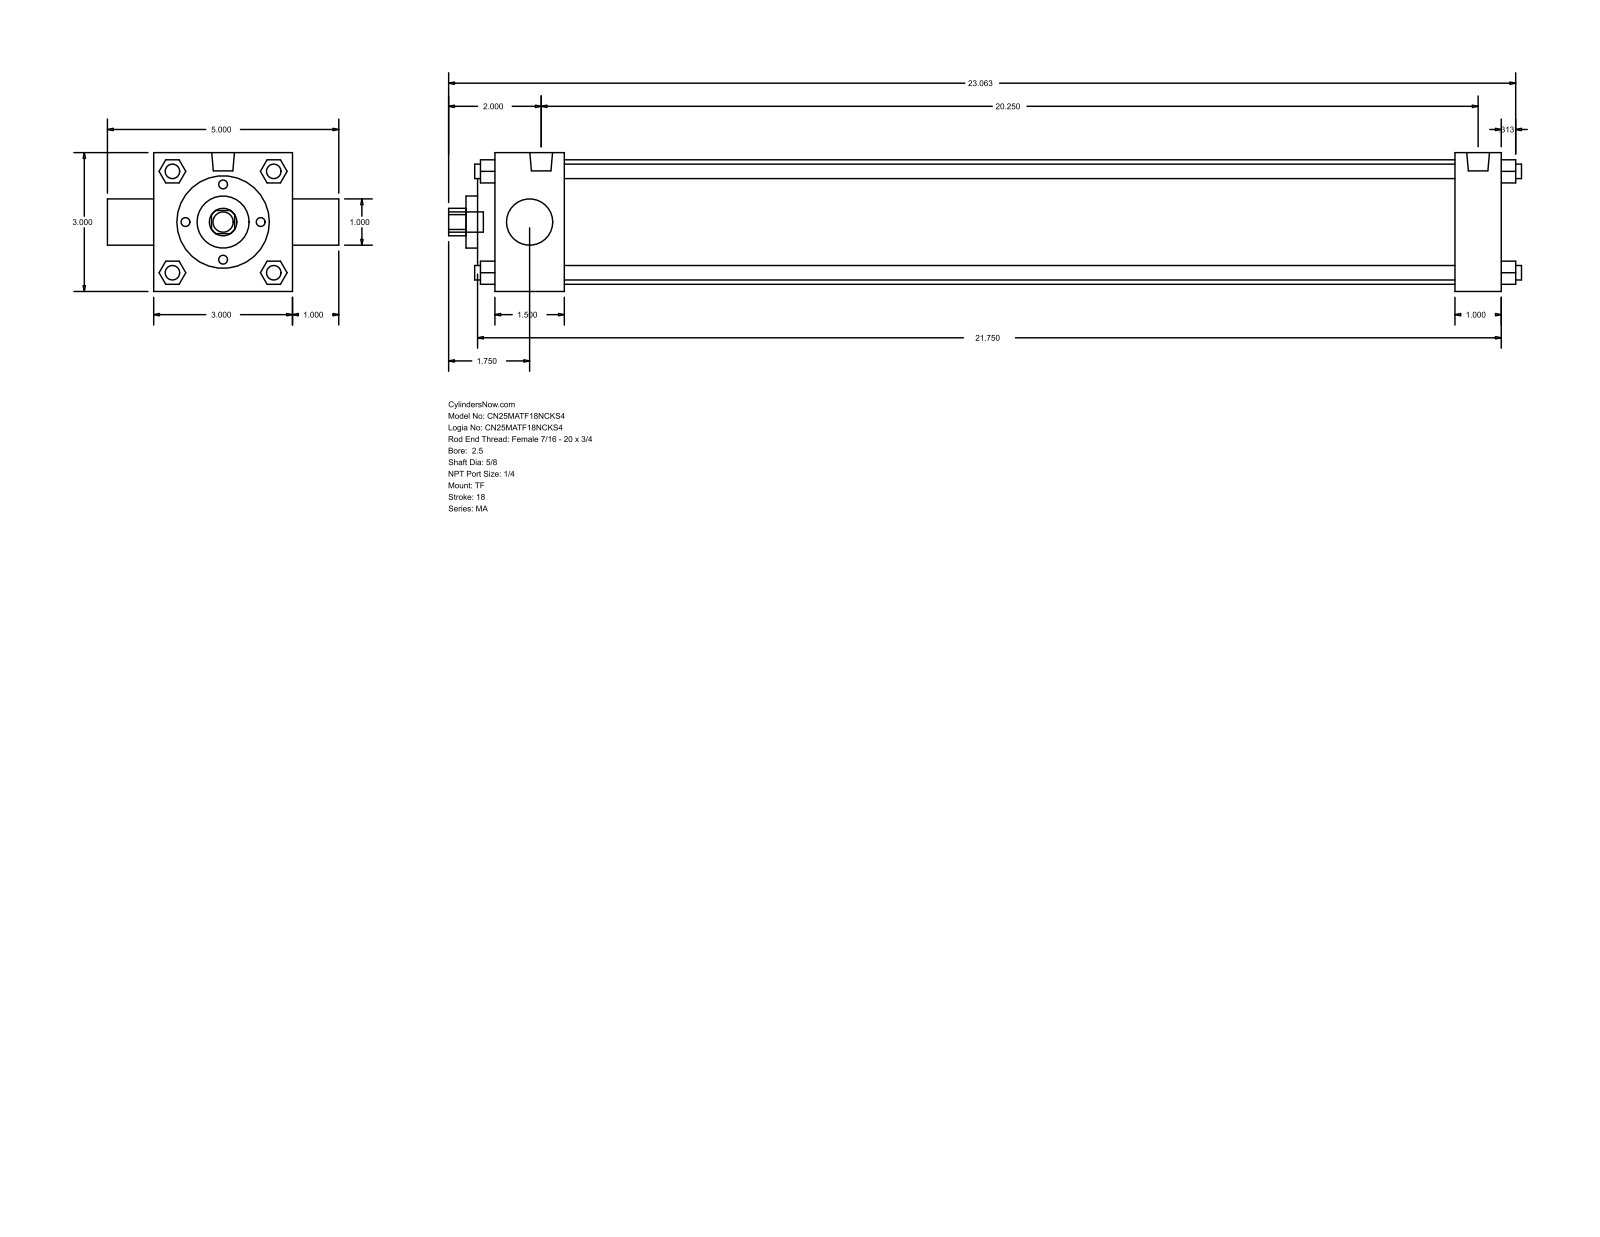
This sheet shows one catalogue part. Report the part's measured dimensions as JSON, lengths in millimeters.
{"part_name": "MA_TF__0250_0.625", "step_written_by": "GSSL Pune (CONFIG_CONTROL_DESIGN)", "units": "millimeters", "bodies": {"solids": 0, "faces": 122, "planar": 93, "cylindrical": 29, "other": 0}, "overall_size": [588.96, 127, 76.2], "round_holes": [[15.88, 1], [25.4, 1], [28.57, 1], [50.8, 1], [68.33, 1]], "round_bosses_or_shafts": [[7.94, 7], [12.49, 2], [11.11, 1]], "partial_cylinders_radius": [[7.54, 1]], "face_to_face_distances": [76.2, 552.45, 25.4, 38.1, 527.05, 488.95, 514.35, 12.7, 9.52, 47.62]}
